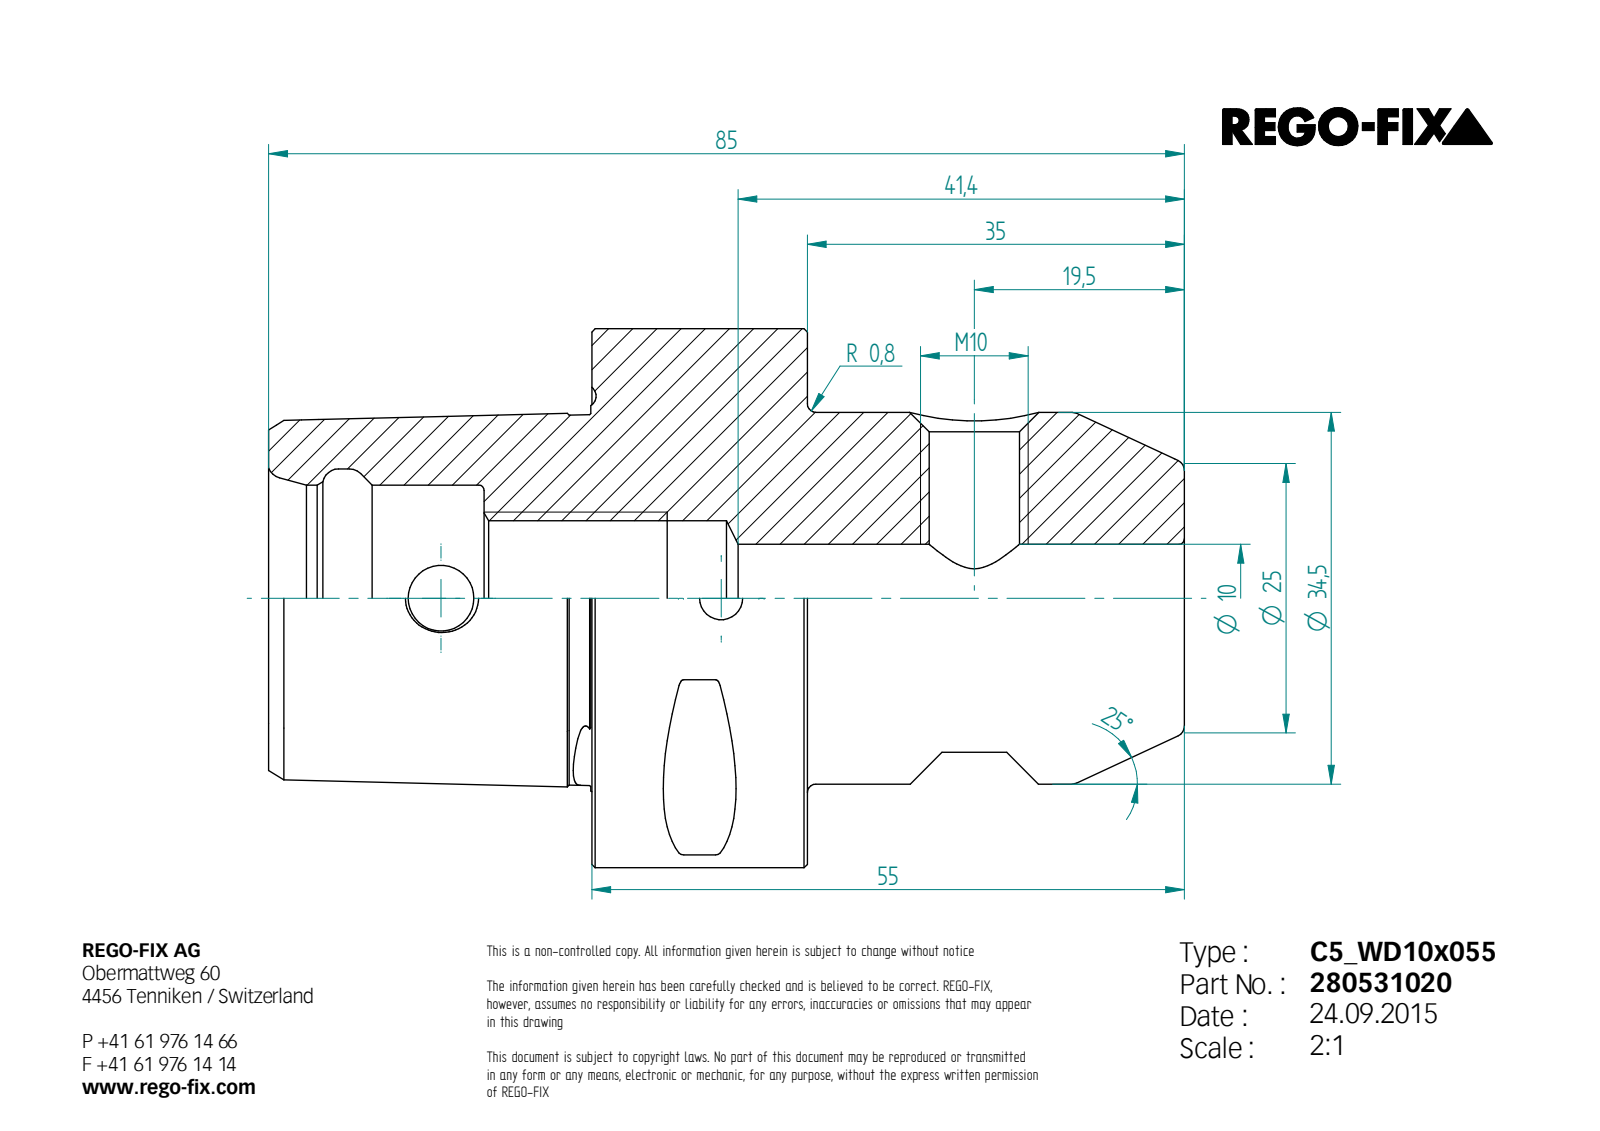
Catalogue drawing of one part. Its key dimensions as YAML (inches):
step_written_by: "Unknown (AUTOMOTIVE_DESIGN)"
units: inches
bodies: {solids: 1, faces: 96, planar: 23, cylindrical: 20, other: 53}
overall_size: [3.346, 1.969, 1.969]
volume: 4.888
surface_area: 27.09
round_holes:
  - {diameter: 0.157, count: 1}
  - {diameter: 0.24, count: 1}
  - {diameter: 0.33, count: 1}
  - {diameter: 0.394, count: 1}
  - {diameter: 0.566, count: 1}
  - {diameter: 0.827, count: 1}
  - {diameter: 0.945, count: 1}
round_bosses_or_shafts:
  - {diameter: 1.969, count: 1}
  - {diameter: 1.358, count: 1}
partial_cylinders:
  - {radius: 0.02, count: 8}
face_to_face_distances: [0.787, 1.181, 2.165, 1.378, 1.969, 3.346, 0.755, 1.748, 0.394, 2.559]
hole_center_spacings: [1.024]
